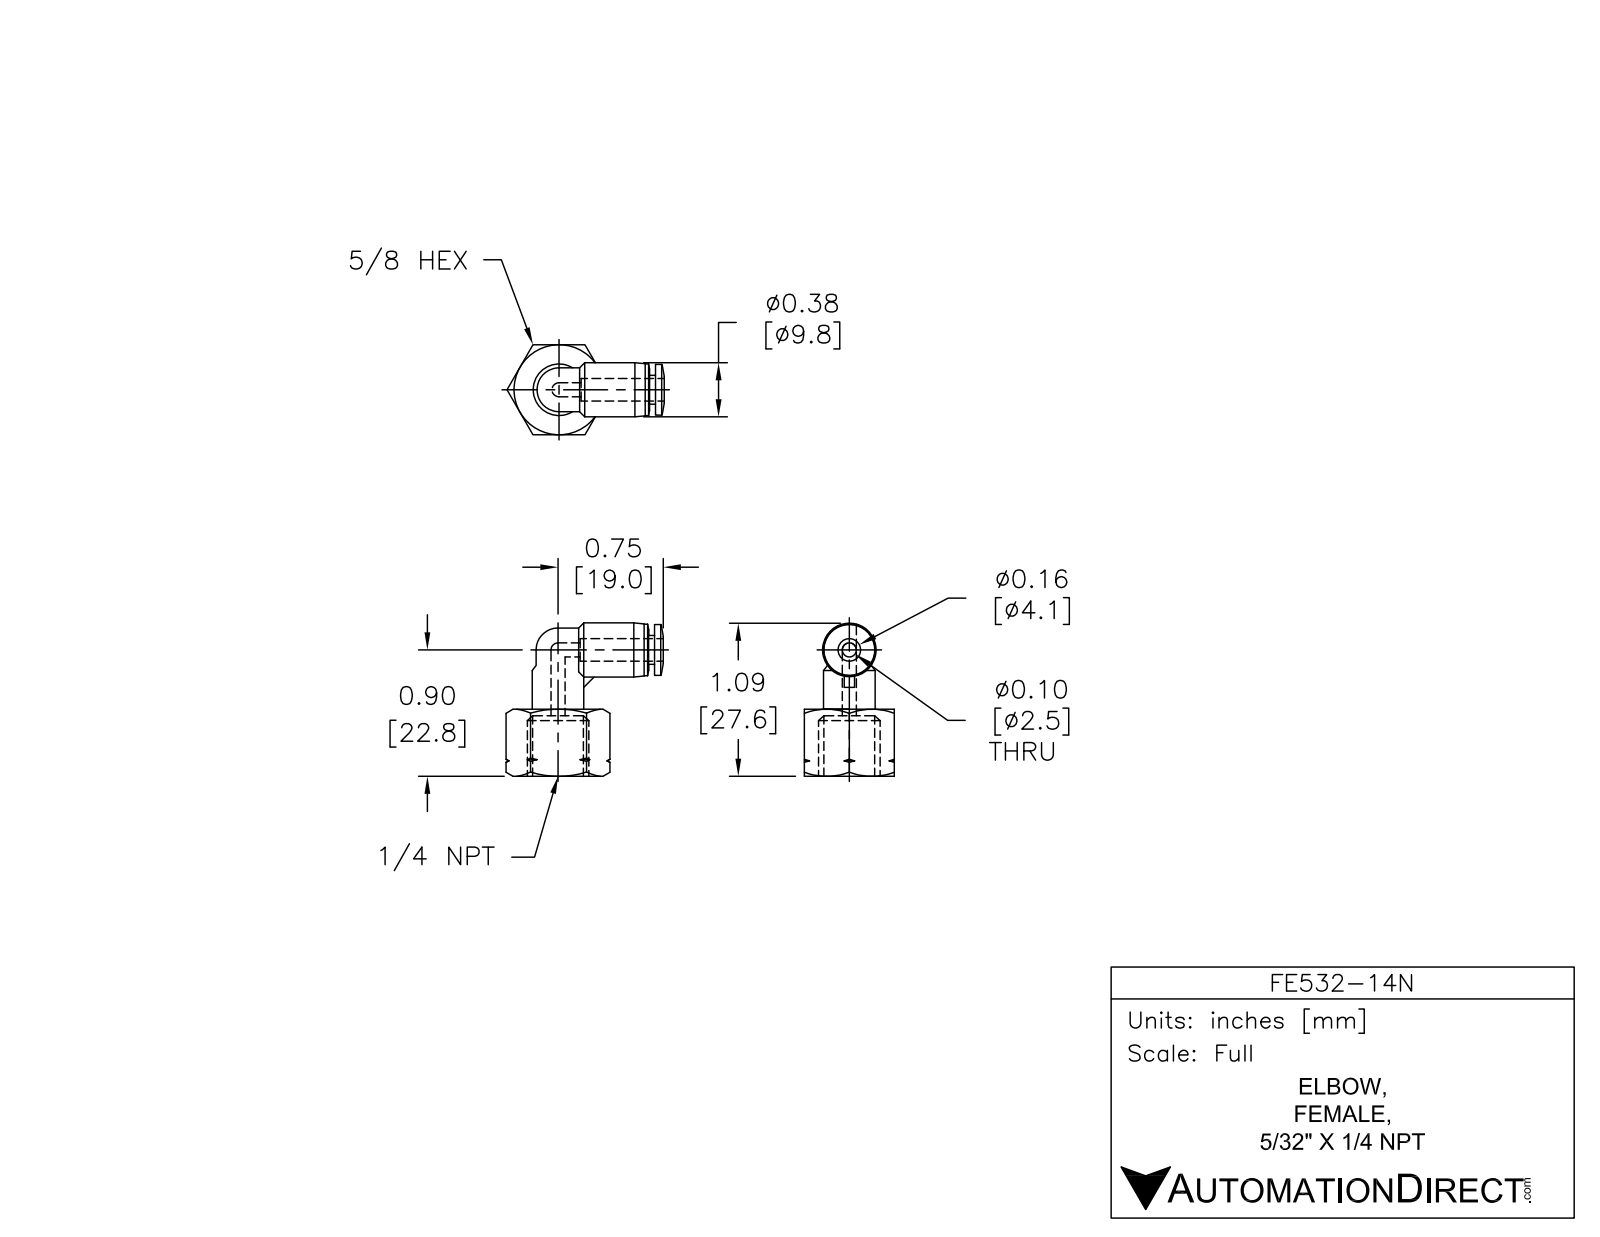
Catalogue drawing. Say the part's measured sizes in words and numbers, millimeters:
The part is named "FE532-14N". Its 3-D file was written by "SolidWorks 2015 (AUTOMOTIVE_DESIGN)". It is 1 solid with 87 faces: 16 planar, 21 cylindrical and 50 other. Overall it measures 29.7 by 28.6 by 17.4 millimeters. Its volume is 3 740 cubic millimeters and its surface area 3 048 square millimeters. Round holes: 2 of diameter 2.5, 1 of diameter 4.3. Round bosses or shafts: 2 of diameter 10, 1 of diameter 10.5, 1 of diameter 9.9, 1 of diameter 5.6. Partial cylindrical surfaces (rounded edges, fillets, slot ends): 2 of radius 4.2. The main face-to-face distances are 17.4, 2, 11, 13, 1.1, 11.9, 13.1, 7.7, 9.7, 11.1.
